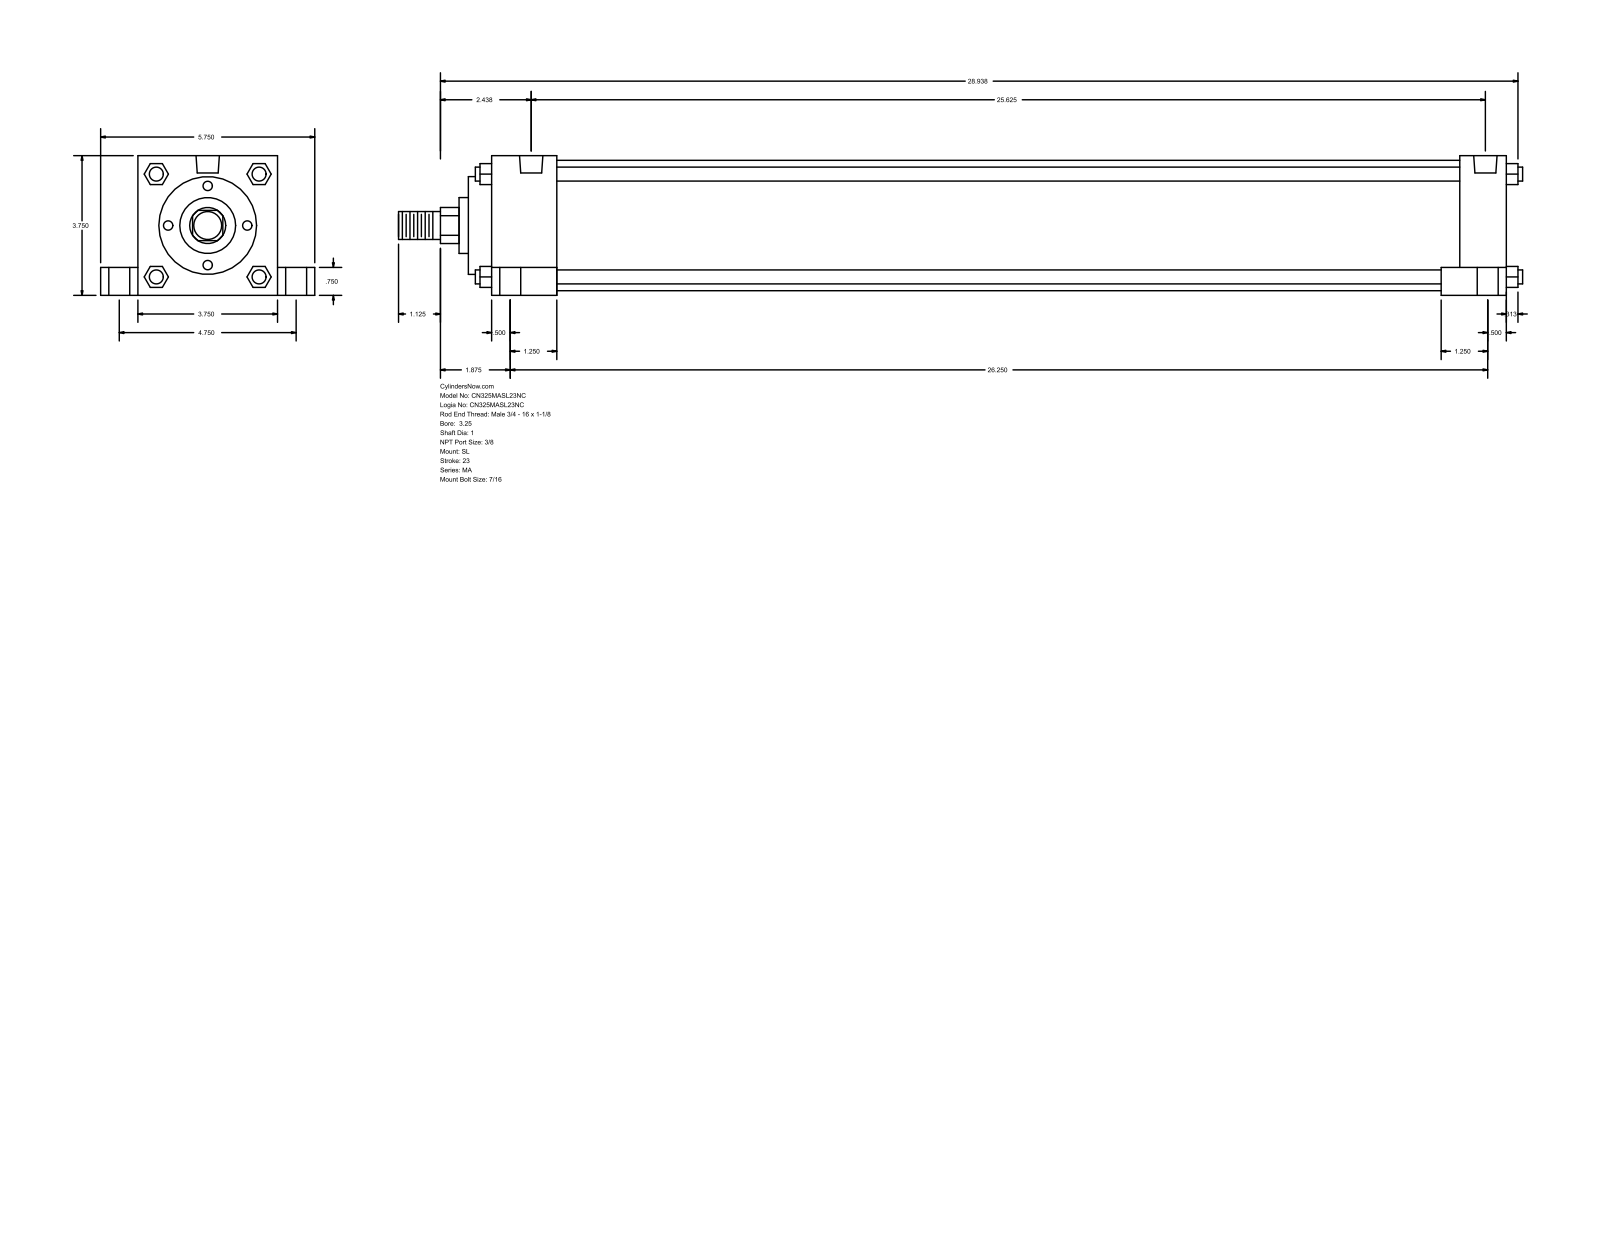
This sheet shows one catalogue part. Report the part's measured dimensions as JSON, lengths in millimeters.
{"part_name": "MA_SL__0325_1", "step_written_by": "GSSL Pune (CONFIG_CONTROL_DESIGN)", "units": "millimeters", "bodies": {"solids": 0, "faces": 150, "planar": 113, "cylindrical": 37, "other": 0}, "overall_size": [766.76, 146.05, 95.25], "round_holes": [[11.11, 4], [14.29, 4], [20.64, 4], [15.93, 2]], "round_bosses_or_shafts": [[9.53, 4], [88.9, 1], [66.67, 1], [38.1, 1], [25.4, 1], [19.05, 1]], "partial_cylinders_radius": [[12.29, 1]], "face_to_face_distances": [95.24, 692.16, 615.95, 15.87, 25.41, 120.65, 19.05, 660.41, 31.75, 44.46], "hole_center_spacings": [60.35, 60.66, 62, 63.27, 120.66, 641.35, 650.51, 655.25]}
